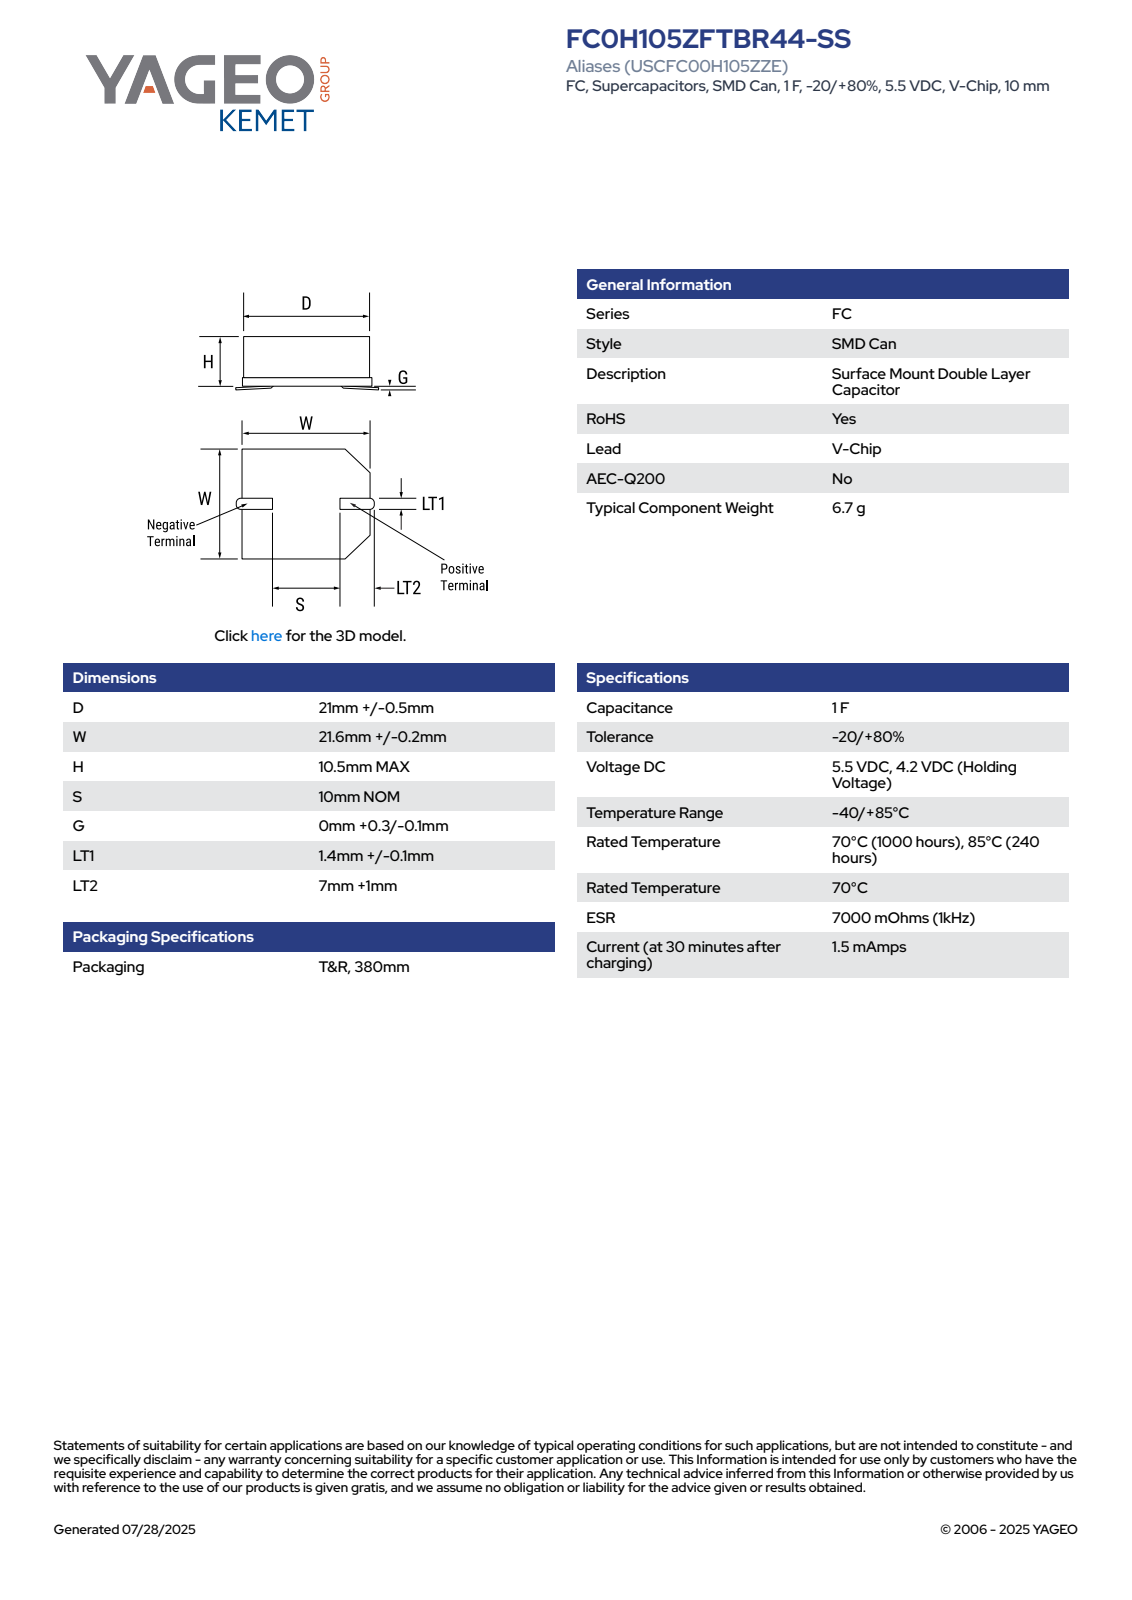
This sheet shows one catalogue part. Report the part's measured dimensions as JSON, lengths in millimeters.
{"part_name": "CDC_VC_D21L10.5LT11.5G0.3W21.8LT28", "step_written_by": "SolidWorks 2014 (AUTOMOTIVE_DESIGN)", "units": "millimeters", "bodies": {"solids": 5, "faces": 60, "planar": 49, "cylindrical": 5, "other": 6}, "overall_size": [26, 21.8, 10.51], "volume_mm3": 3795, "surface_area_mm2": 2379, "round_bosses_or_shafts": [[21, 1]], "partial_cylinders_radius": [[0.2, 2], [8.34, 1]], "face_to_face_distances": [2.62, 10.2, 7.58, 21.8, 2.92, 10.5, 10.15, 11.65, 1.5, 2.1]}
